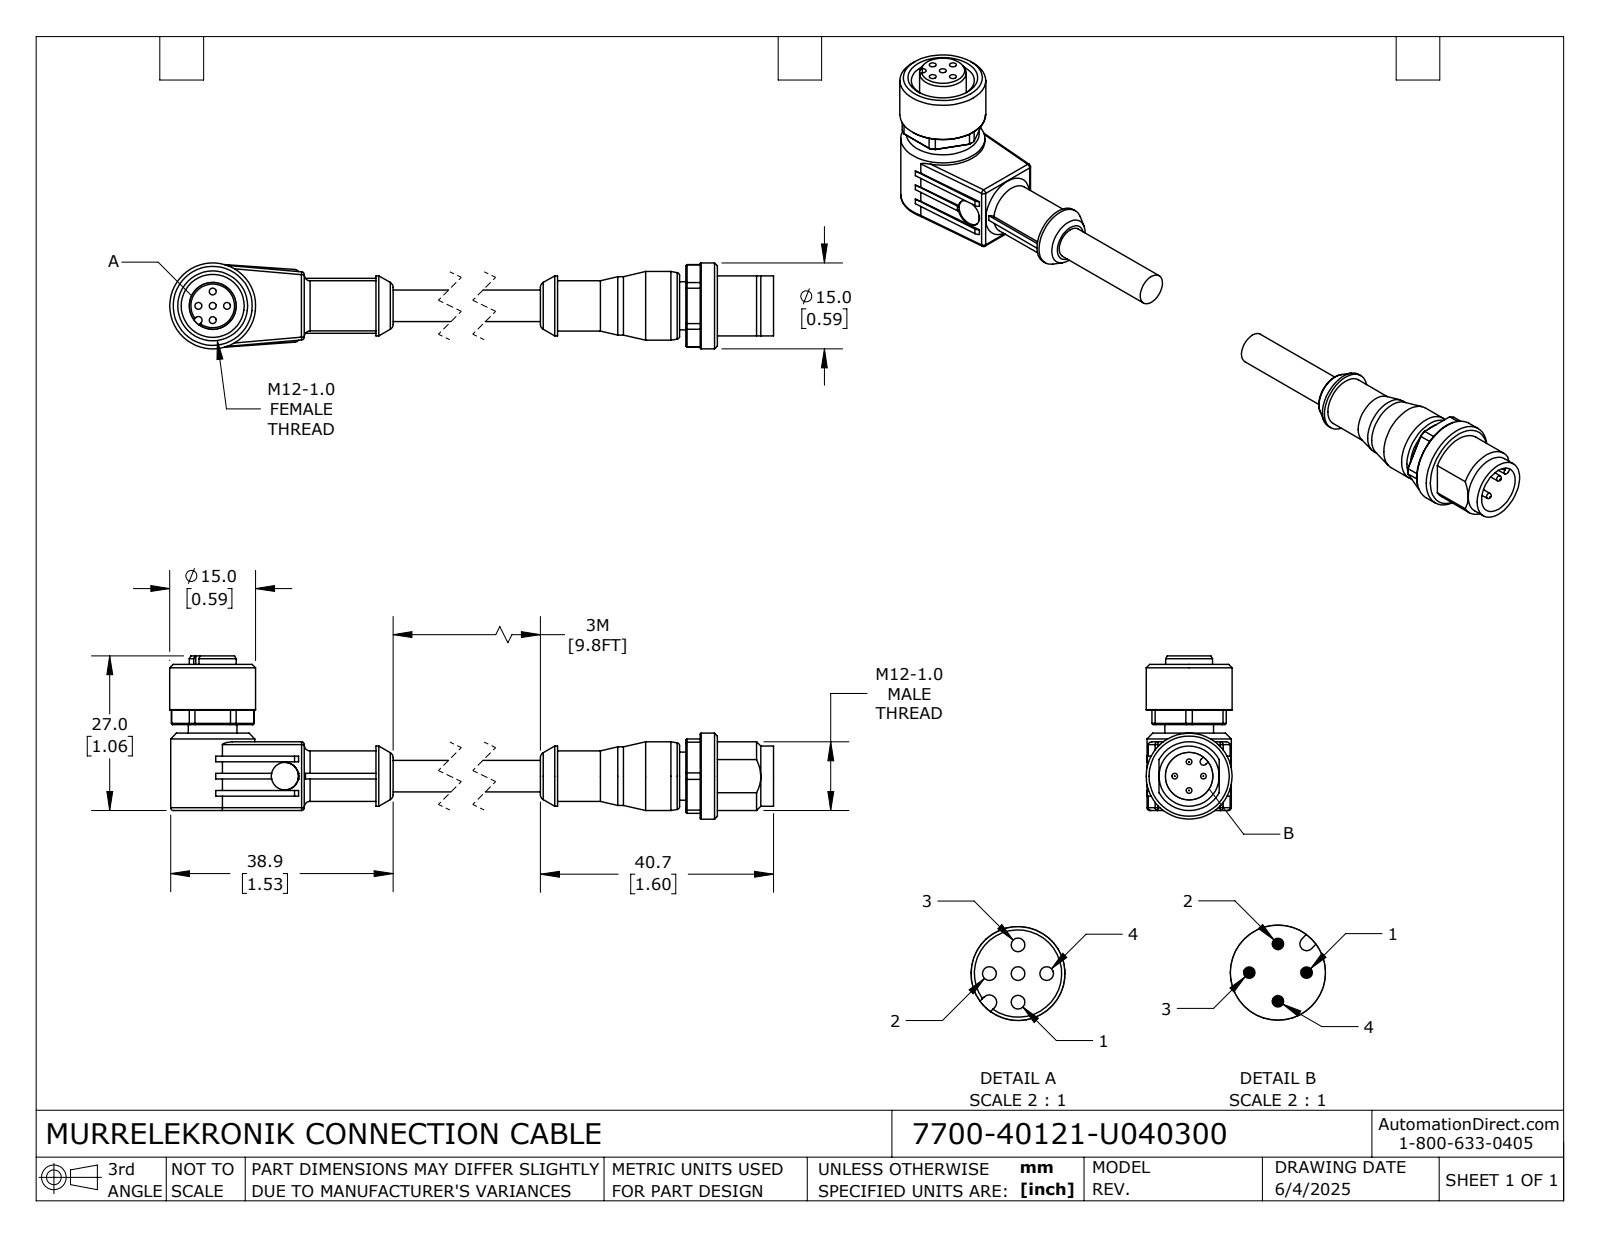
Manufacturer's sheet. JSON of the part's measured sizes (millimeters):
{"part_name": "7700-40121-U040300; 7700-40121-U040300_FEMALE; 7700-40121-U040300_MALE", "step_written_by": "SolidWorks 2024 (CONFIG_CONTROL_DESIGN)", "units": "millimeters", "bodies": {"solids": 2, "faces": 248, "planar": 91, "cylindrical": 95, "other": 62}, "overall_size": [144.7, 28.5, 15], "volume_mm3": 10768, "surface_area_mm2": 6089, "round_holes": [[1.2, 5], [4.8, 1], [8.3, 1], [11, 1]], "round_bosses_or_shafts": [[1, 4], [15, 2], [14.7, 1], [12, 1], [10.5, 1], [10.2, 1], [8.8, 1], [8.5, 1]], "partial_cylinders_radius": [[0.5, 8], [1, 2], [7.2, 2], [0.6, 1], [0.65, 1]], "face_to_face_distances": [3, 12, 1.5, 13.5, 5.5, 15, 13, 6, 10.5, 2.5], "hole_center_spacings": [2.5, 3.54, 5]}
